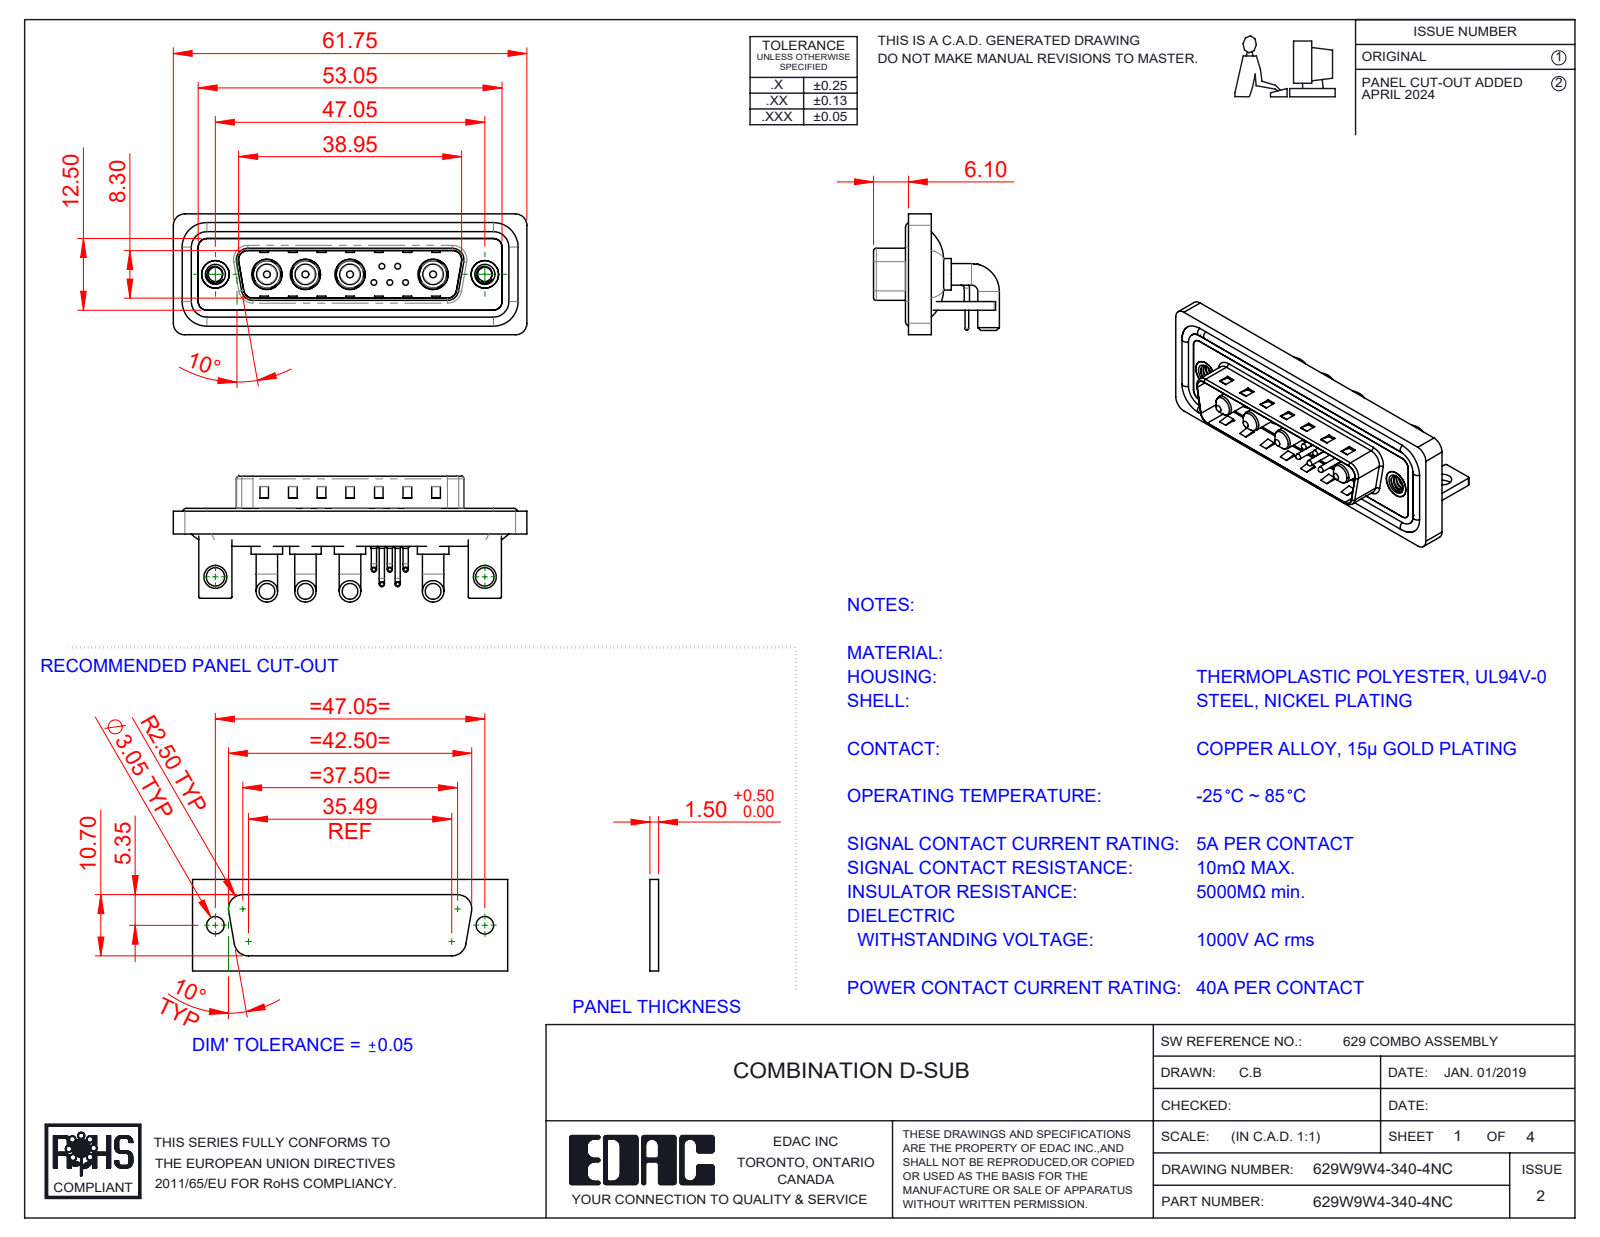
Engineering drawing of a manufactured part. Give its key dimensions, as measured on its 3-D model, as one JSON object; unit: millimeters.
{"part_name": "629Combo Threaded Rivet_B; 629Combo Stabilizer Bracket; 629Combo Housing_9W4; 629W9W4-340-4NC (+6 more)", "step_written_by": "SolidWorks 2023 (CONFIG_CONTROL_DESIGN)", "units": "millimeters", "bodies": {"solids": 22, "faces": 1243, "planar": 589, "cylindrical": 470, "other": 184}, "overall_size": [61.75, 21.98, 21.1], "volume_mm3": 8268, "surface_area_mm2": 13140, "round_holes": [[0.75, 5], [1.6, 5], [2, 5], [4.85, 4], [5.3, 4], [2.5, 2], [3.2, 2], [4, 2], [4.8, 2], [5, 2]], "round_bosses_or_shafts": [[0.9, 10], [3.75, 8], [1.5, 5], [1, 5], [0.65, 5], [5.5, 4], [5.2, 4], [4.75, 4]], "partial_cylinders_radius": [[2, 19], [1.5, 18], [0.25, 16], [0.5, 9], [1.6, 8], [1.01, 5], [0.6, 4], [0.65, 4]], "face_to_face_distances": [0.4, 1.5, 0.8, 2.9, 2.1, 1.1, 3.7, 4.1, 4.5, 1.6], "hole_center_spacings": [3.16, 2.77, 5.04, 14.5, 47.05, 2.78, 4.4, 4.41]}
